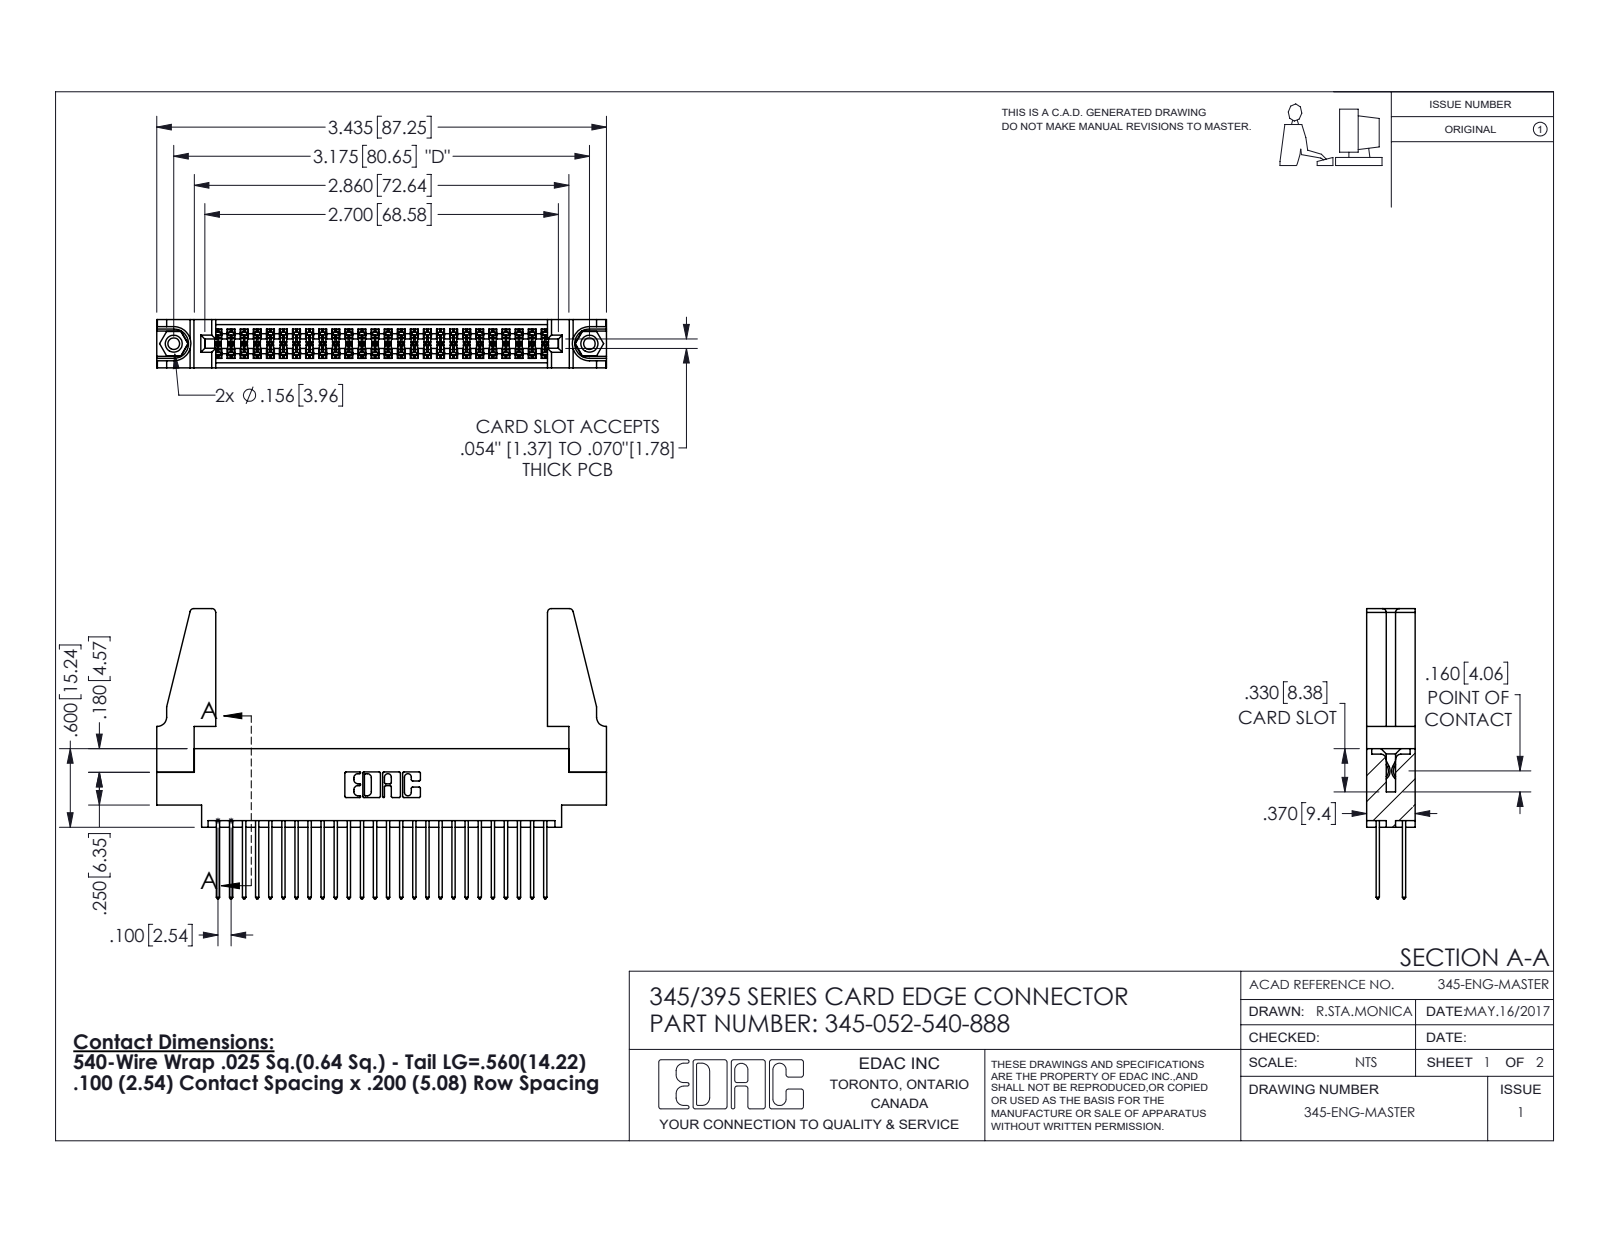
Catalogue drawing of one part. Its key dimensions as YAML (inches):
part_name: "345-220-078_345-220-088; 345-250-001_345-250-001-102; 345-052-540-888; 345-292-001_345-293-140 (+1 more)"
step_written_by: "SolidWorks 2016 (CONFIG_CONTROL_DESIGN)"
units: inches
bodies: {solids: 57, faces: 2854, planar: 1872, cylindrical: 966, other: 16}
overall_size: [3.436, 2.217, 0.37]
volume: 0.712
surface_area: 25.27
round_holes:
  - {diameter: 0.089, count: 2}
  - {diameter: 0.125, count: 2}
  - {diameter: 0.156, count: 2}
  - {diameter: 0.064, count: 1}
round_bosses_or_shafts:
  - {diameter: 0.155, count: 2}
partial_cylinders:
  - {radius: 0.006, count: 78}
  - {radius: 0.01, count: 52}
  - {radius: 0.01, count: 22}
  - {radius: 0.03, count: 8}
  - {radius: 0.007, count: 6}
  - {radius: 0.031, count: 6}
  - {radius: 0.026, count: 3}
  - {radius: 0.014, count: 2}
face_to_face_distances: [0.072, 0.298, 0.37, 0.2, 0.098, 0.272, 0.025, 0.225, 0.175, 0.149]
hole_center_spacings: [0.27, 2.94, 3.175]
